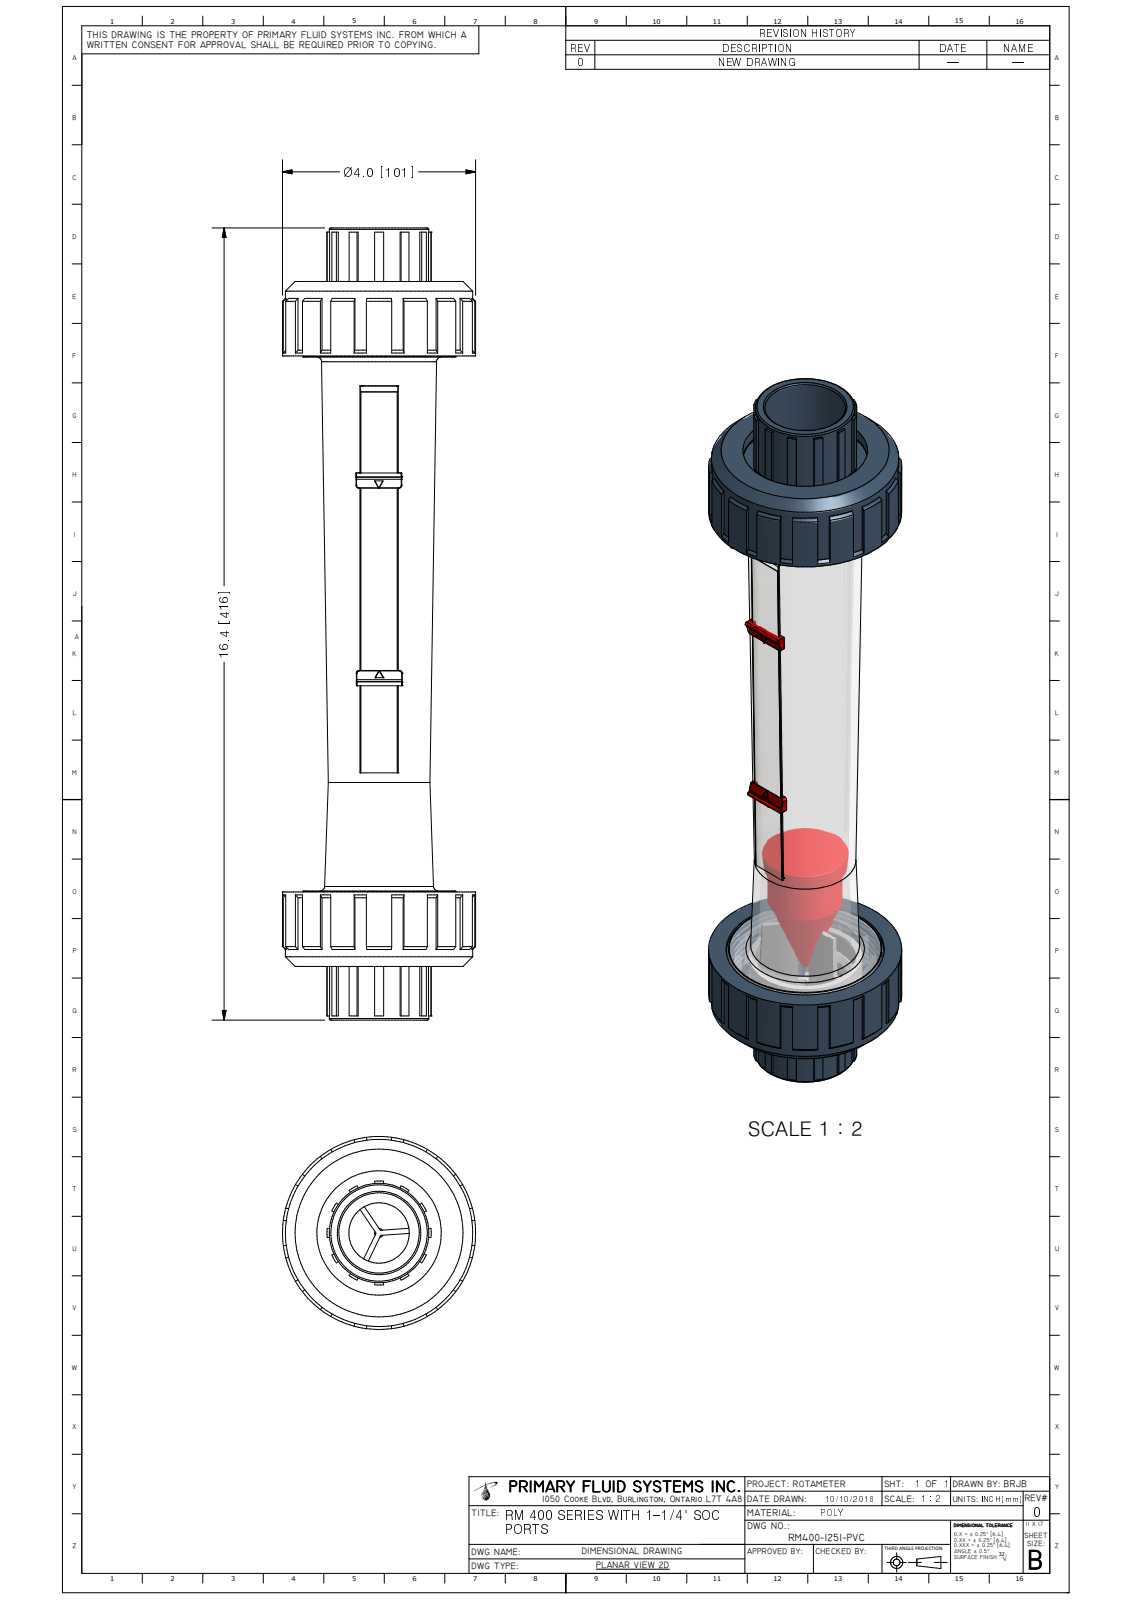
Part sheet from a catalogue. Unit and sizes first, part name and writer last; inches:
Units: inches
Overall size (bounding box): 16.378 × 3.99 × 3.99
Round holes (diameter × count): ⌀1.661 ×1, ⌀2.57 ×1, ⌀3.147 ×1, ⌀3.265 ×1, ⌀3.265 ×1
Round bosses / shafts (diameter × count): ⌀3.99 ×1, ⌀3.87 ×1, ⌀3.158 ×1, ⌀2.984 ×1, ⌀2.055 ×1
Partial cylindrical surfaces — rounded edges, fillets, slot ends (radius × count): R0.008 ×18, R0.01 ×16, R0.004 ×8, R0.006 ×8, R0.06 ×4, R0.008 ×2, R0.04 ×2, R1.077 ×1
Main face-to-face distances: 1.54, 12.623, 1.561, 12.602, 0.021, 11.061, 0.3, 13.863, 1.24, 1.261
Volume: 79.21 in³ · Surface area: 276.8 in²
Bodies: 1 solid, 649 faces (261 planar, 128 cylindrical, 260 other)
Part name (STEP PRODUCT): RM400-125I-PVC_R0
STEP written by: Autodesk Inventor 2009 (AUTOMOTIVE_DESIGN)
